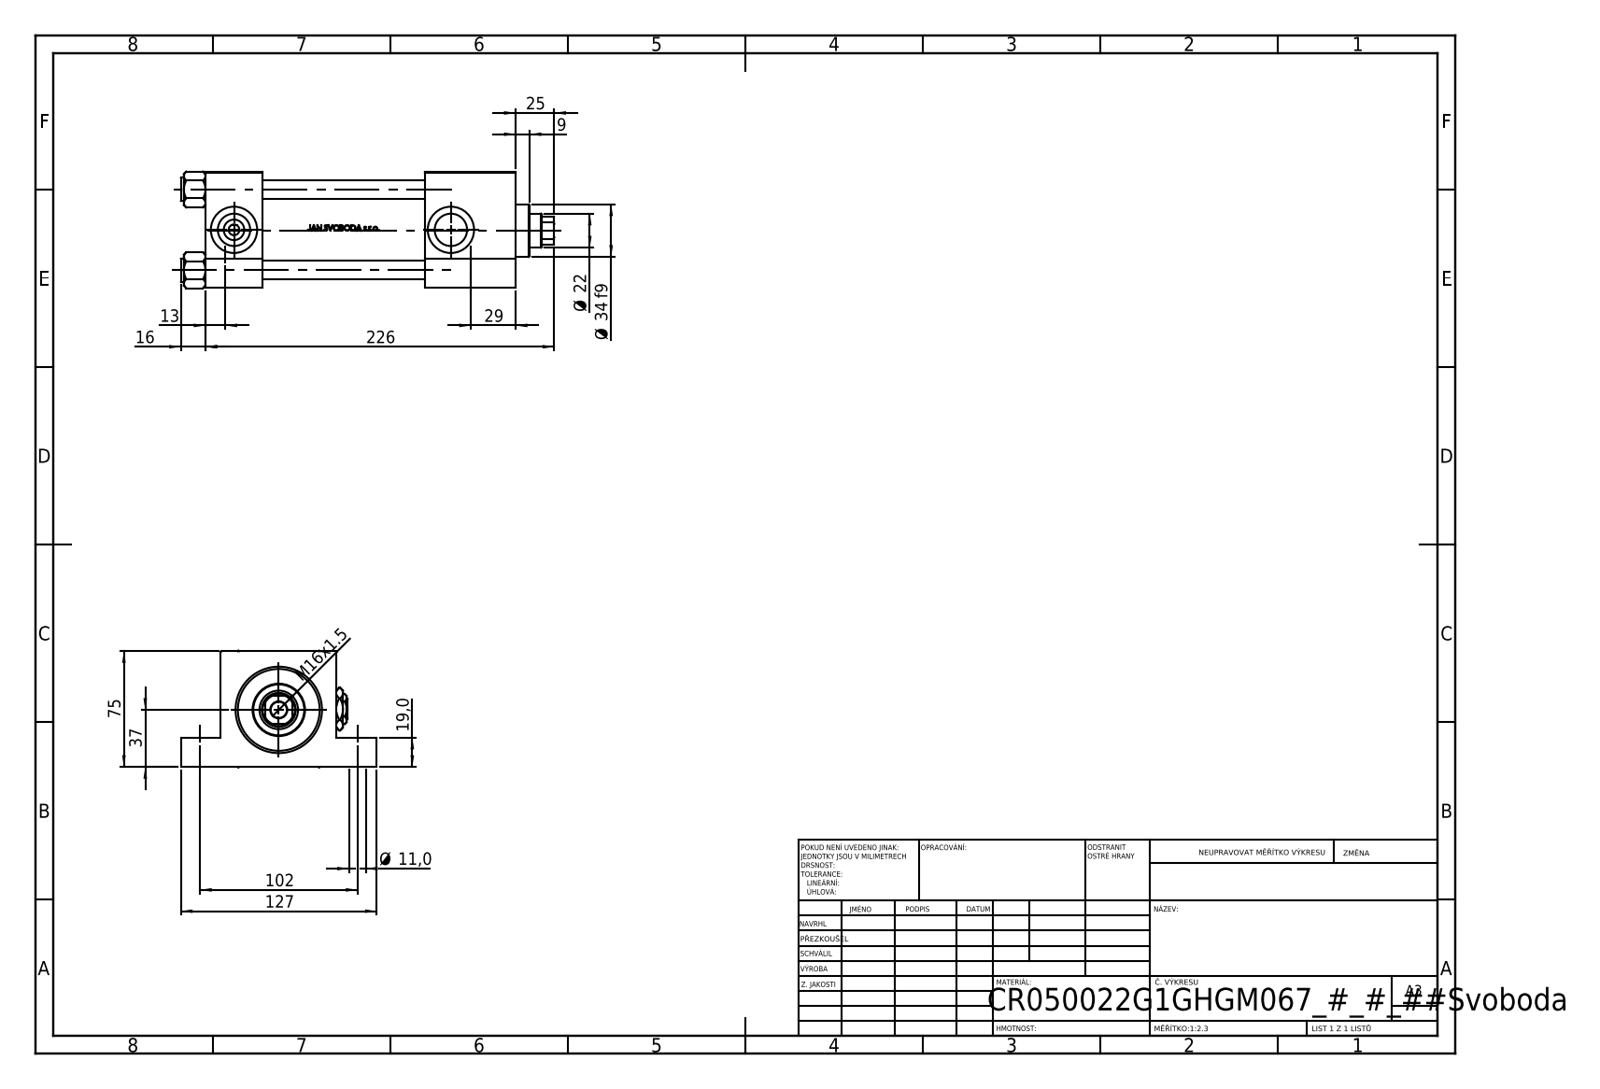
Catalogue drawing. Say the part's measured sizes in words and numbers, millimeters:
The part is named "V215CR_G_Body; Zatka_pro_OIL_PORT; NUT_M5_G; V215_VC_A (+2 more)". Its 3-D file was written by "SolidWorks 2019 (CONFIG_CONTROL_DESIGN)". It is 12 solids with 1134 faces: 454 planar, 128 cylindrical and 552 other. Overall it measures 242 by 127 by 75.54 millimeters. Its volume is 815 009 cubic millimeters and its surface area 187 291 square millimeters. Round holes: 4 of diameter 11, 4 of diameter 12, 2 of diameter 7, 2 of diameter 20.96, 2 of diameter 30, 1 of diameter 10.5, 1 of diameter 22, 1 of diameter 25, 1 of diameter 41, 1 of diameter 50, 1 of diameter 53. Round bosses or shafts: 4 of diameter 15, 1 of diameter 56, 1 of diameter 34. Partial cylindrical surfaces (rounded edges, fillets, slot ends): 1 of radius 10.5. The main face-to-face distances are 75, 37, 201, 164, 19, 56, 142, 105, 59, 26. The hole center spacings are 52.3, 36.63, 37.34, 73.96, 102, 159, 188.9, 140.5.
